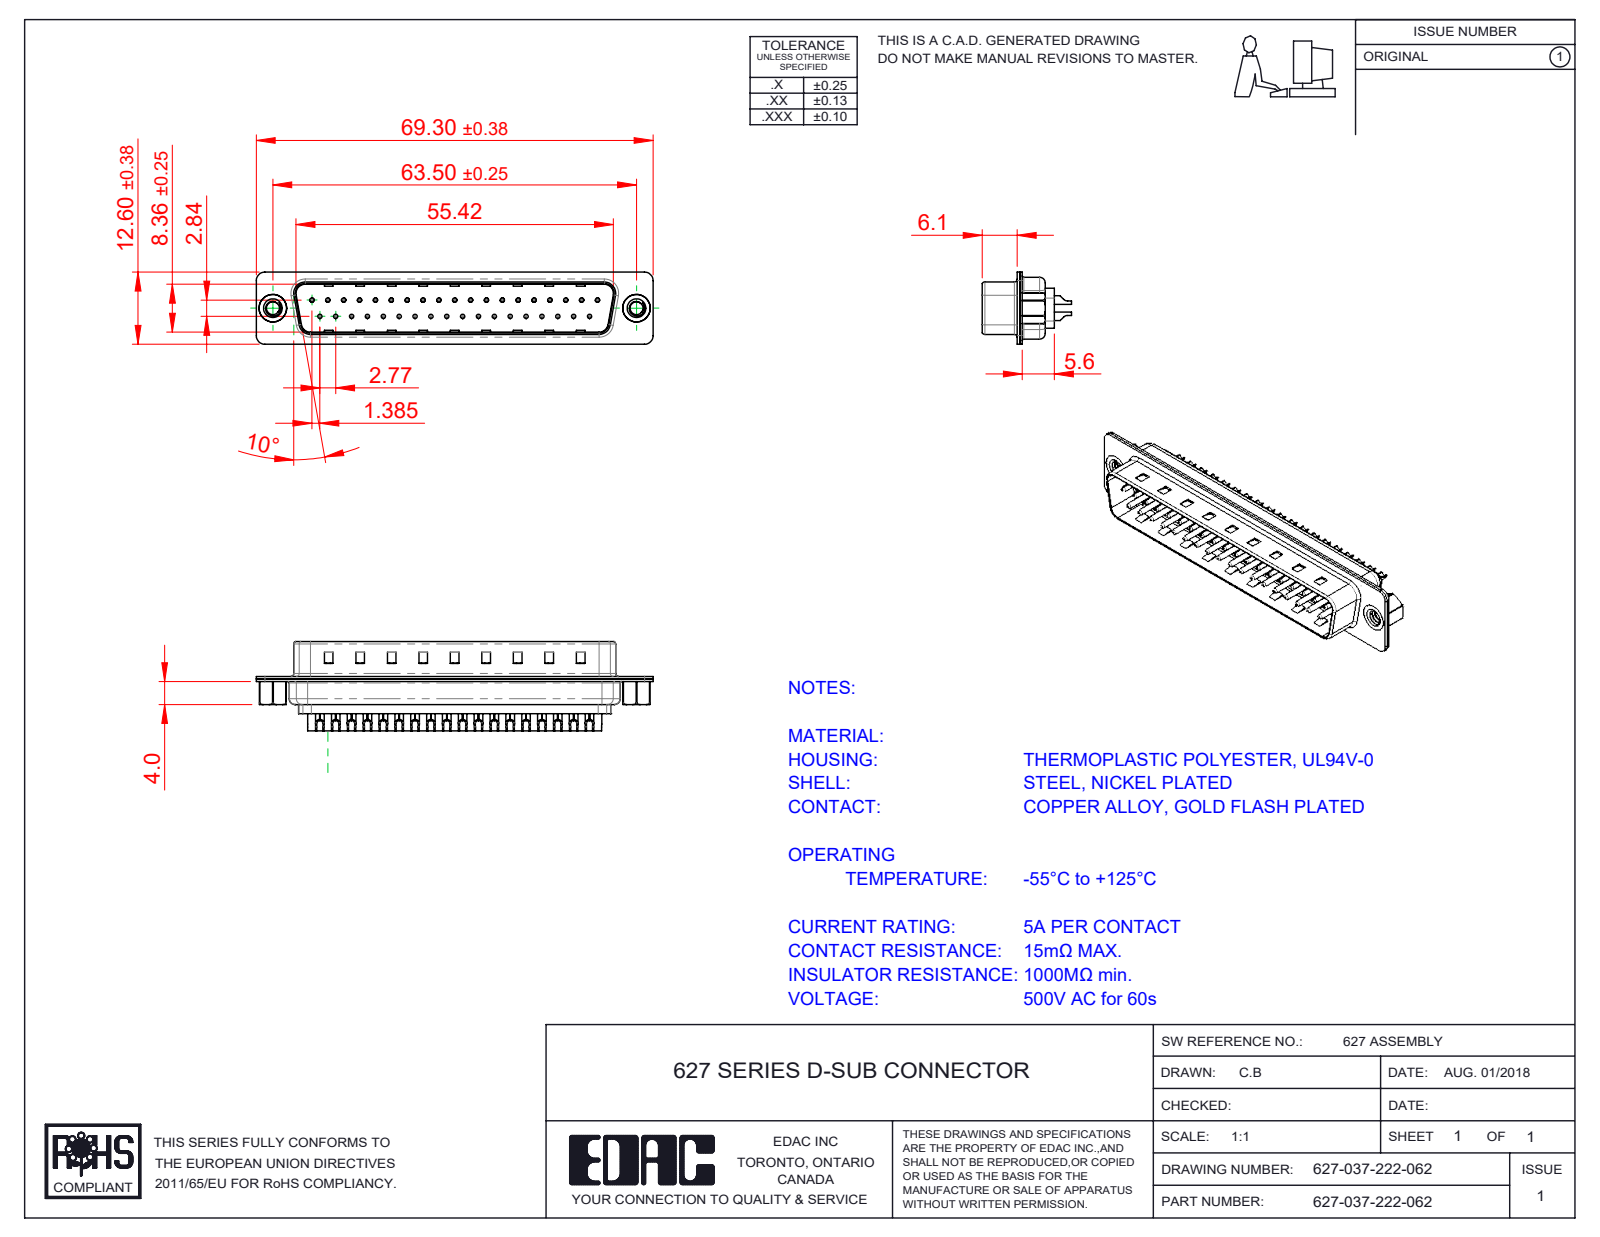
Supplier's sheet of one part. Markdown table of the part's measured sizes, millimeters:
| quantity | value |
| --- | --- |
| part name | 627 Contact Row 2_22L; 627 Contact Row 1_22L; 627-037-222-062; 627 Shell Front_37 Contacts (+3 more) |
| STEP written by | SolidWorks 2020 (CONFIG_CONTROL_DESIGN) |
| units | millimeters |
| bodies | 42 solids, 2776 faces (721 planar, 1212 cylindrical, 843 other) |
| overall size | 69.3 × 15.35 × 12.6 |
| volume | 3 709 mm³ |
| surface area | 10 747 mm² |
| round holes (diameter × count) | 0.35 × 37, 1.1 × 37, 1.6 × 37, 2.26 × 2, 4 × 2, 4.8 × 2 |
| round bosses / shafts (diameter × count) | 2 × 37, 1.5 × 37, 0.75 × 37, 5 × 2, 4.9 × 2 |
| partial cylindrical surfaces (radius × count) | 1.5 × 16, 2 × 12, 0.5 × 8, 1.6 × 8, 1 × 6, 0.25 × 4, 0.6 × 4, 0.65 × 4 |
| main face-to-face distances | 0.4, 0.82, 9.58, 0.45, 8.76, 1.5, 0.9, 1.4, 6.05, 0.42 |
| hole center spacings | 3.16, 2.77, 5.54, 8.31, 5.04, 10.1, 11.08, 12.78 |
